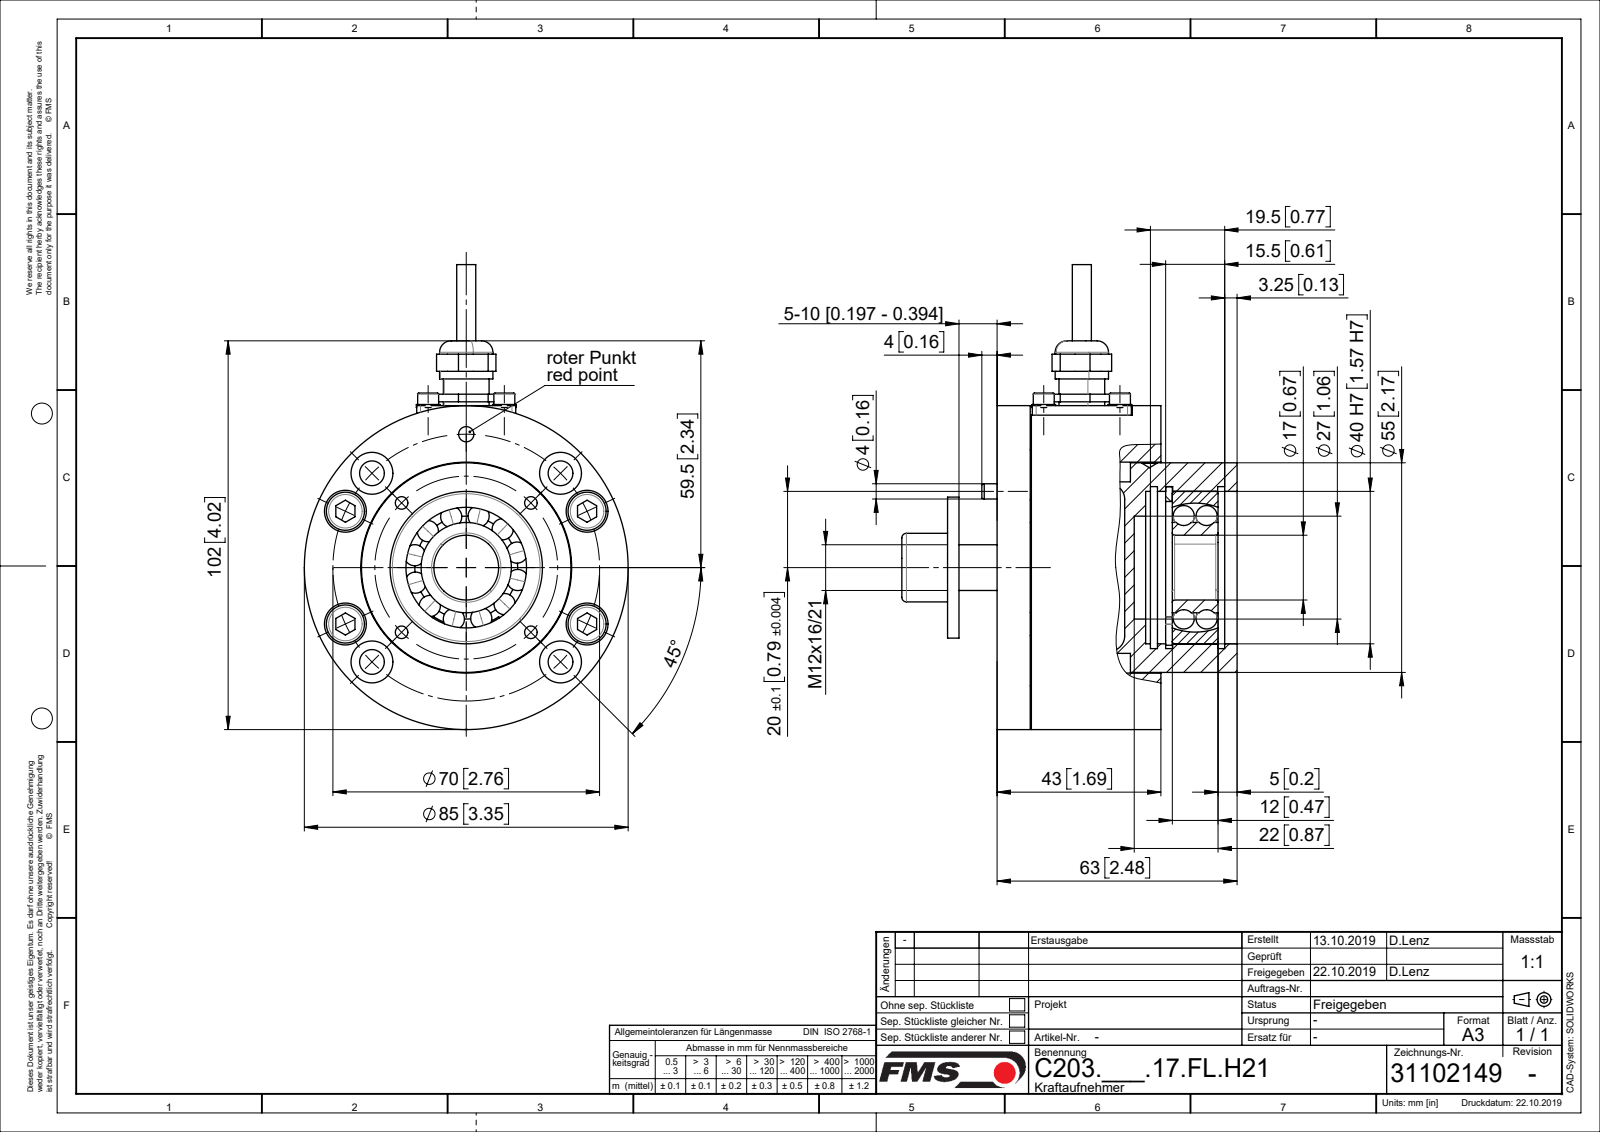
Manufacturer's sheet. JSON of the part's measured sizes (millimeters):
{"part_name": "ZEICHNUNG5; ZEICHNUNG4; C1105272; C1105271 (+8 more)", "step_written_by": "Mechanical Desktop 2009 (CONFIG_CONTROL_DESIGN)", "units": "millimeters", "bodies": {"solids": 24, "faces": 485, "planar": 170, "cylindrical": 235, "other": 80}, "overall_size": [100.5, 85, 67], "volume_mm3": 244557, "surface_area_mm2": 80043, "round_holes": [[6.5, 8], [11, 8], [2.6, 4], [3.2, 4], [3.42, 4], [5.15, 4], [7, 4], [4, 1], [6, 1], [10.68, 1], [15, 1], [17, 1]], "round_bosses_or_shafts": [[1.5, 5], [10, 4], [6.2, 4], [6, 4], [5.5, 4], [5, 4], [3, 4], [85, 1]], "partial_cylinders_radius": [[2.5, 4], [5, 2]], "face_to_face_distances": [3, 8.7, 6, 34, 42.7, 4, 43, 9, 58, 15], "hole_center_spacings": [35, 42.44, 20, 11, 12.16, 14.14, 14.91, 24]}
